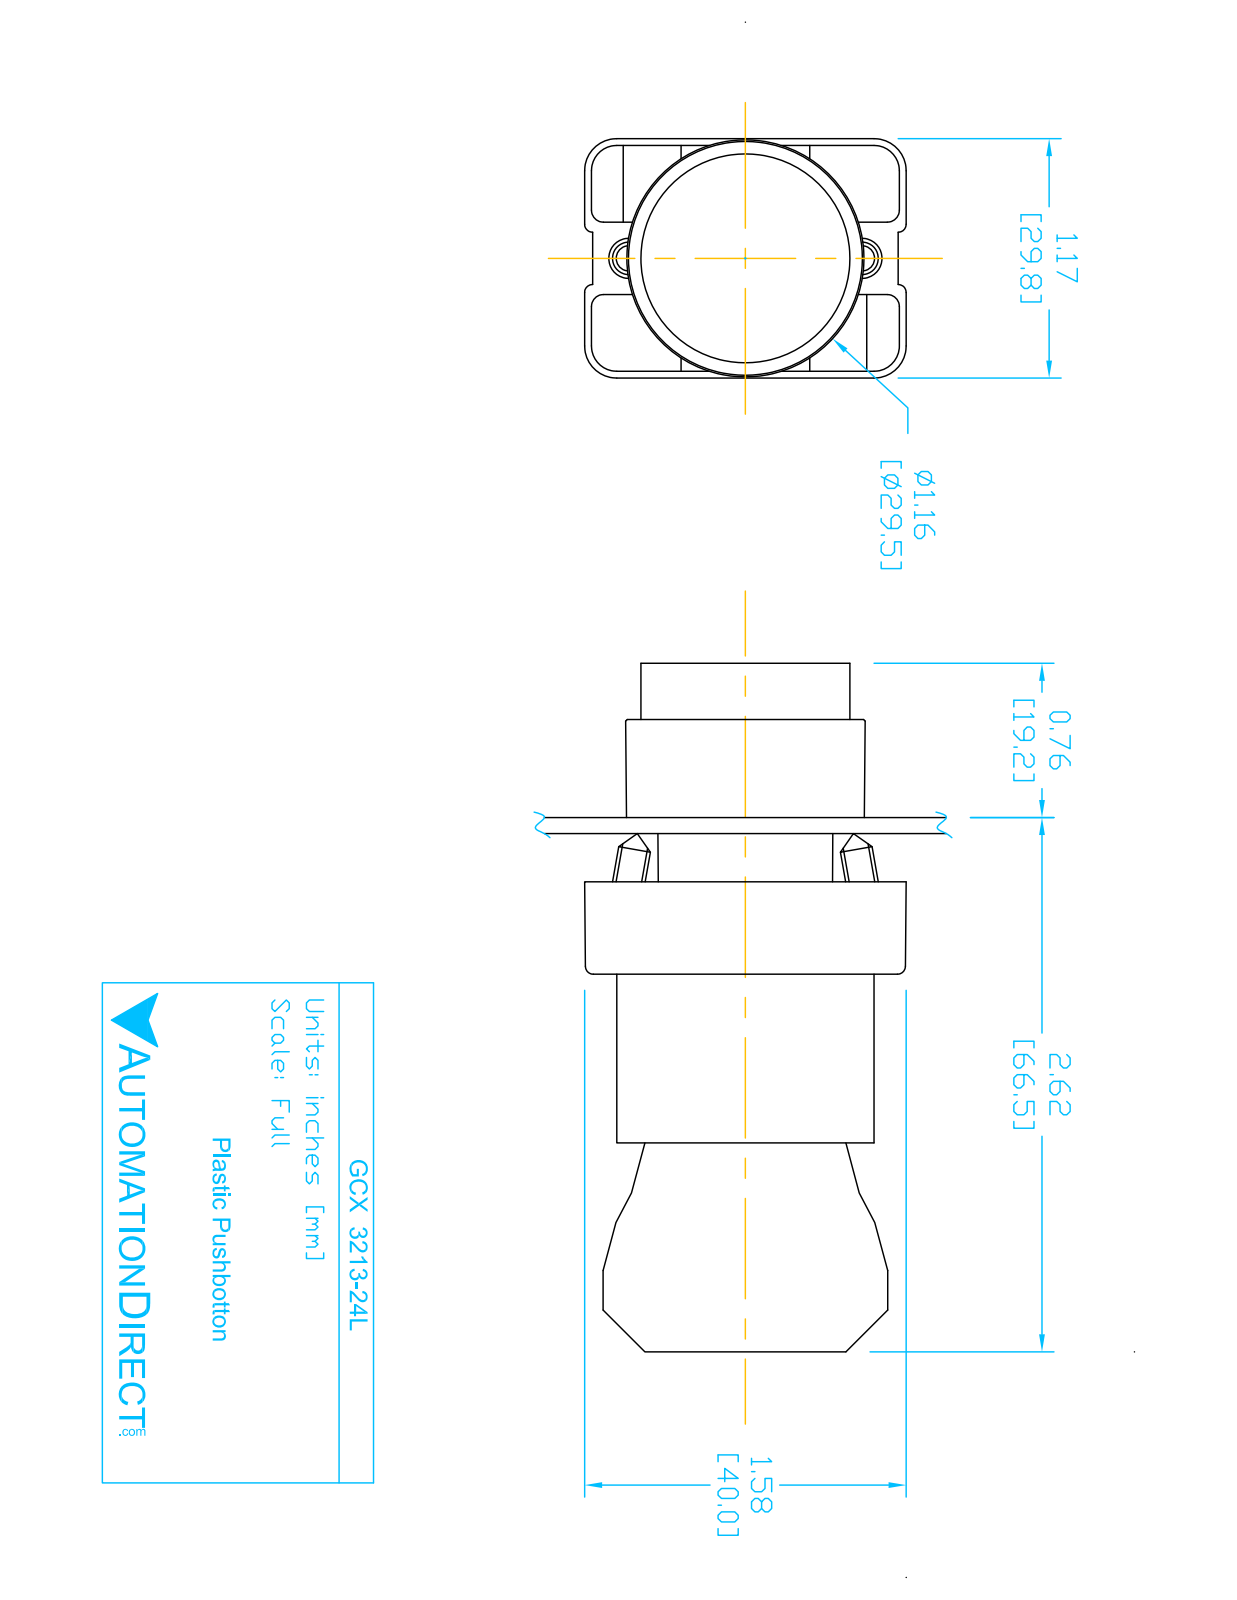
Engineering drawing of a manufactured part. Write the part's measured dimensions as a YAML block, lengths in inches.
part_name: "ECX3029-2; GCX3213-24L; ECX1050; ecx1040 (+1 more)"
step_written_by: "SolidWorks 2016 (AUTOMOTIVE_DESIGN)"
units: inches
bodies: {solids: 7, faces: 425, planar: 250, cylindrical: 144, other: 31}
overall_size: [3.319, 1.581, 1.177]
volume: 2.721
surface_area: 36.32
round_holes:
  - {diameter: 0.079, count: 2}
  - {diameter: 0.124, count: 2}
  - {diameter: 0.13, count: 2}
  - {diameter: 0.087, count: 1}
  - {diameter: 0.197, count: 1}
  - {diameter: 0.469, count: 1}
  - {diameter: 0.878, count: 1}
  - {diameter: 0.888, count: 1}
  - {diameter: 1.024, count: 1}
round_bosses_or_shafts:
  - {diameter: 0.157, count: 4}
  - {diameter: 1.175, count: 1}
  - {diameter: 1.004, count: 1}
  - {diameter: 0.945, count: 1}
  - {diameter: 0.856, count: 1}
  - {diameter: 0.78, count: 1}
  - {diameter: 0.504, count: 1}
partial_cylinders:
  - {radius: 0.059, count: 24}
  - {radius: 0.041, count: 12}
  - {radius: 0.124, count: 12}
  - {radius: 0.157, count: 12}
  - {radius: 0.039, count: 8}
  - {radius: 0.128, count: 2}
  - {radius: 0.02, count: 1}
  - {radius: 0.063, count: 1}
face_to_face_distances: [0.827, 0.579, 1.171, 2.02, 1.193, 0.031, 0.033, 0.573, 1.165, 0.593]
hole_center_spacings: [0.236, 0.544, 0.472, 0.49]
